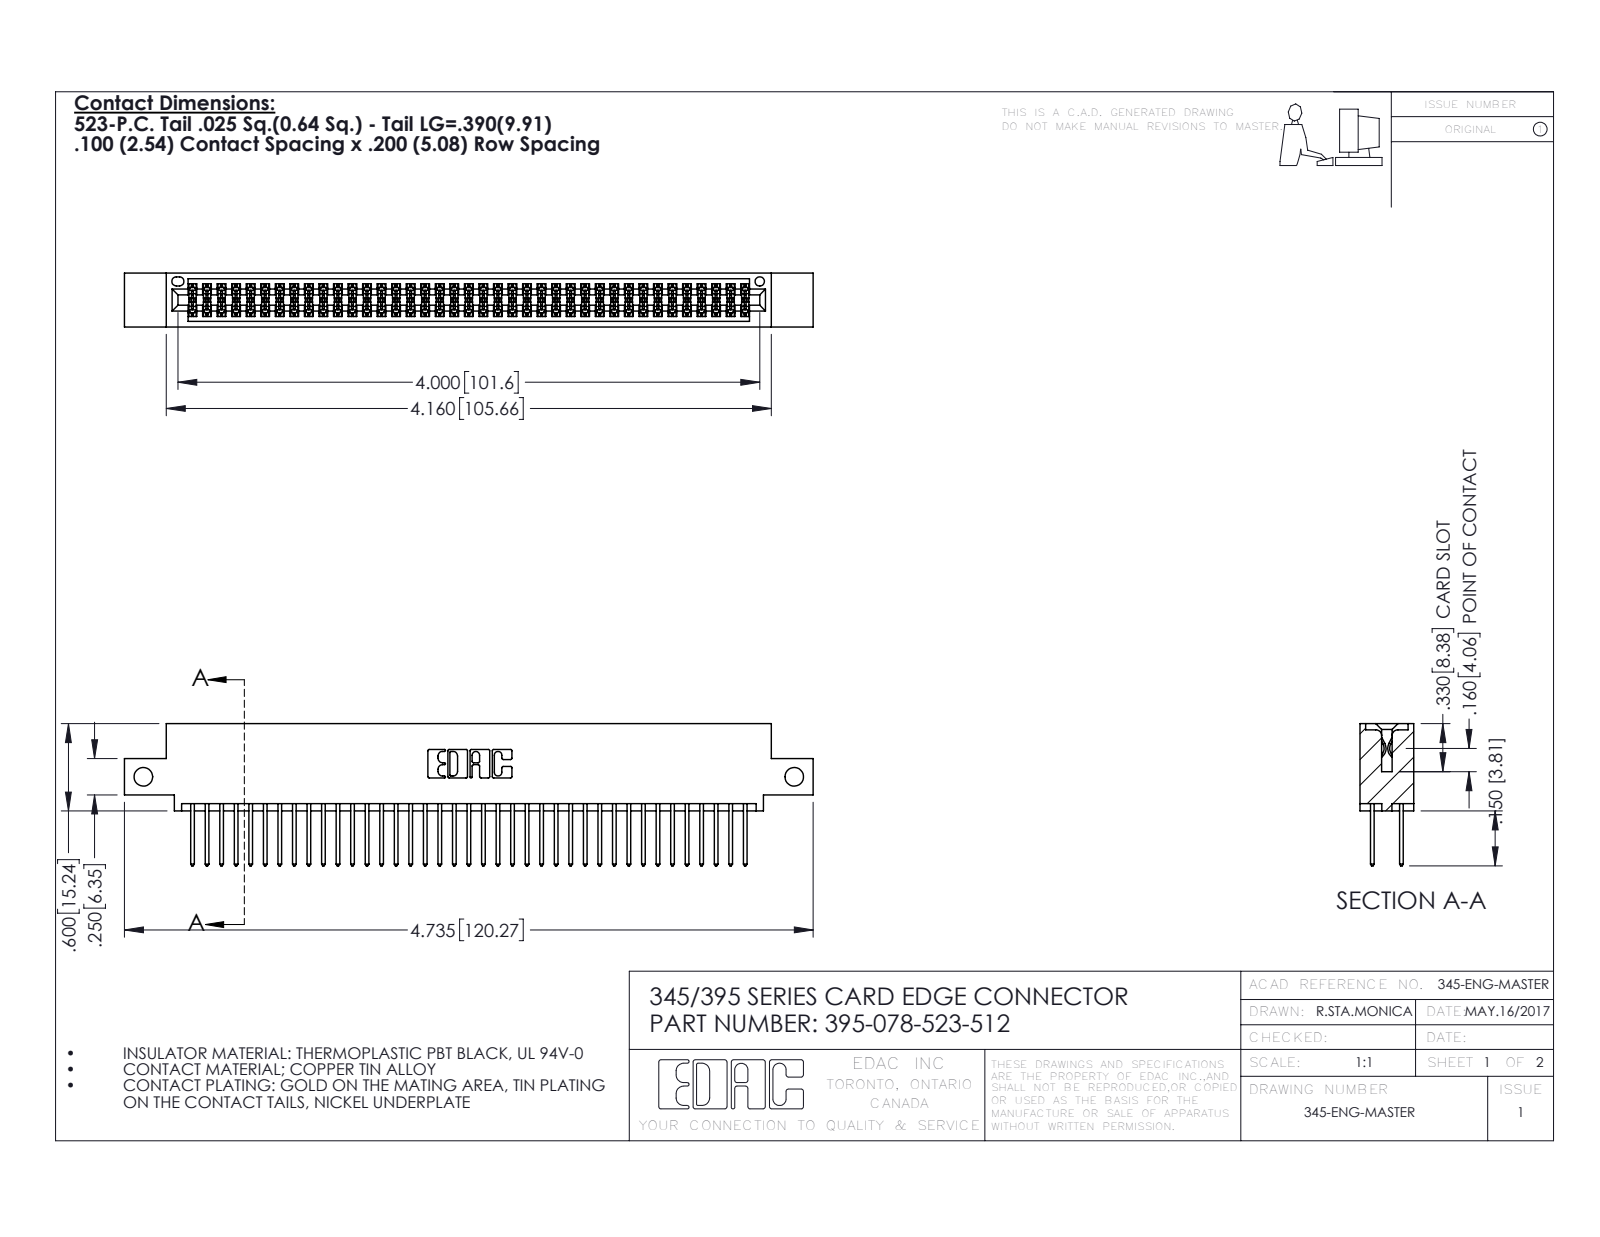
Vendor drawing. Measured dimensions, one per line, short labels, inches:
name: 395-078-523-512; 345-292-001_345-293-123; 345 Part_0.110 Offset - Side Mount
written by: SolidWorks 2016 (CONFIG_CONTROL_DESIGN)
unit: in
bodies: 79 solids, 4030 faces (2658 planar, 1372 cylindrical, 0 other)
size: 4.735 × 0.977 × 0.37
volume: 0.711 in³; area: 27.66 in²
holes: 2× ⌀0.128, 1× ⌀0.064
rounds: 117× R0.006, 78× R0.01, 22× R0.01, 6× R0.007, 6× R0.031, 3× R0.026, 2× R0.014, 2× R0.019
face distances: 0.072, 0.298, 0.2, 0.098, 0.272, 0.025, 0.37, 0.225, 0.175, 0.149
hole spacings: 4.475
